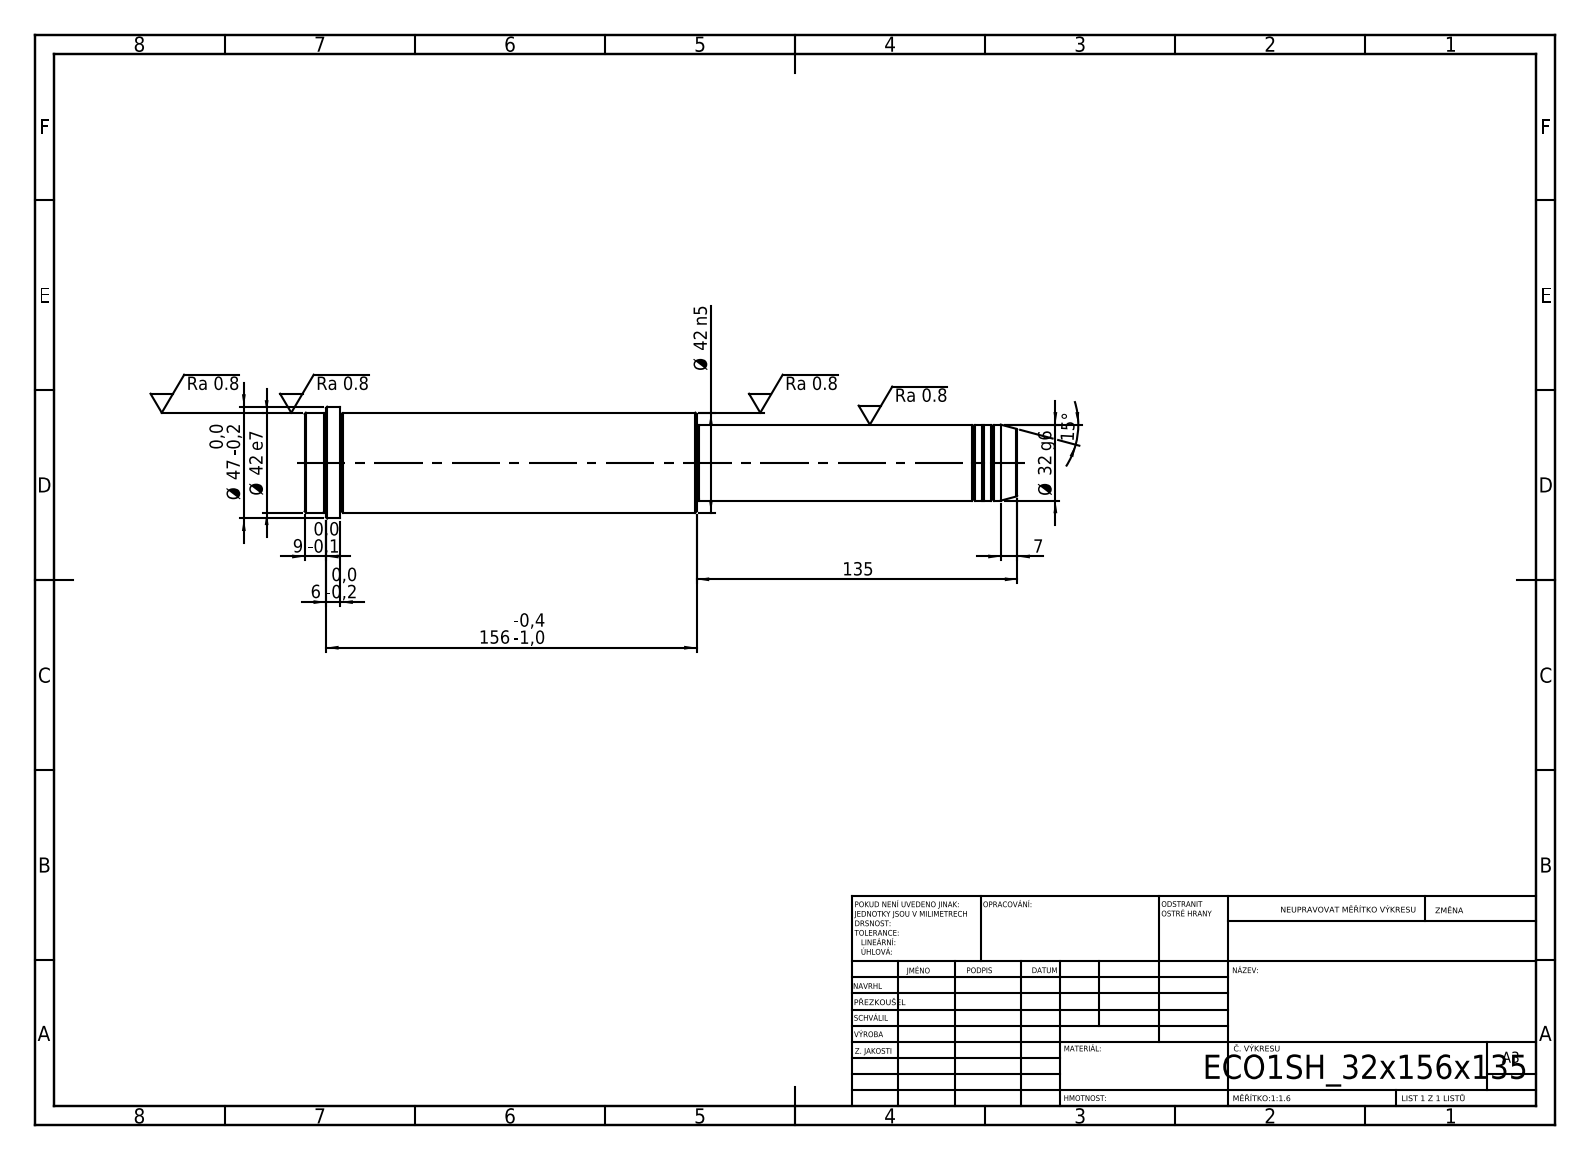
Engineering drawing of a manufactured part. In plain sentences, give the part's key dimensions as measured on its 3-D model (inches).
Its 3-D file was written by "SolidWorks 2019 (CONFIG_CONTROL_DESIGN)". It is 1 solid with 52 faces: 6 planar, 16 cylindrical and 30 other. Overall it measures 11.811 by 1.85 by 1.85 inches. Its volume is 20.65 cubic inches and its surface area 60.42 square inches. Round bosses or shafts: 1 of diameter 1.85, 1 of diameter 1.654, 1 of diameter 1.26, 1 of diameter 1.22. The main face-to-face distances are 11.811, 5.315, 6.496, 11.22, 5.906, 0.591, 11.457, 6.142, 0.236, 0.354.
